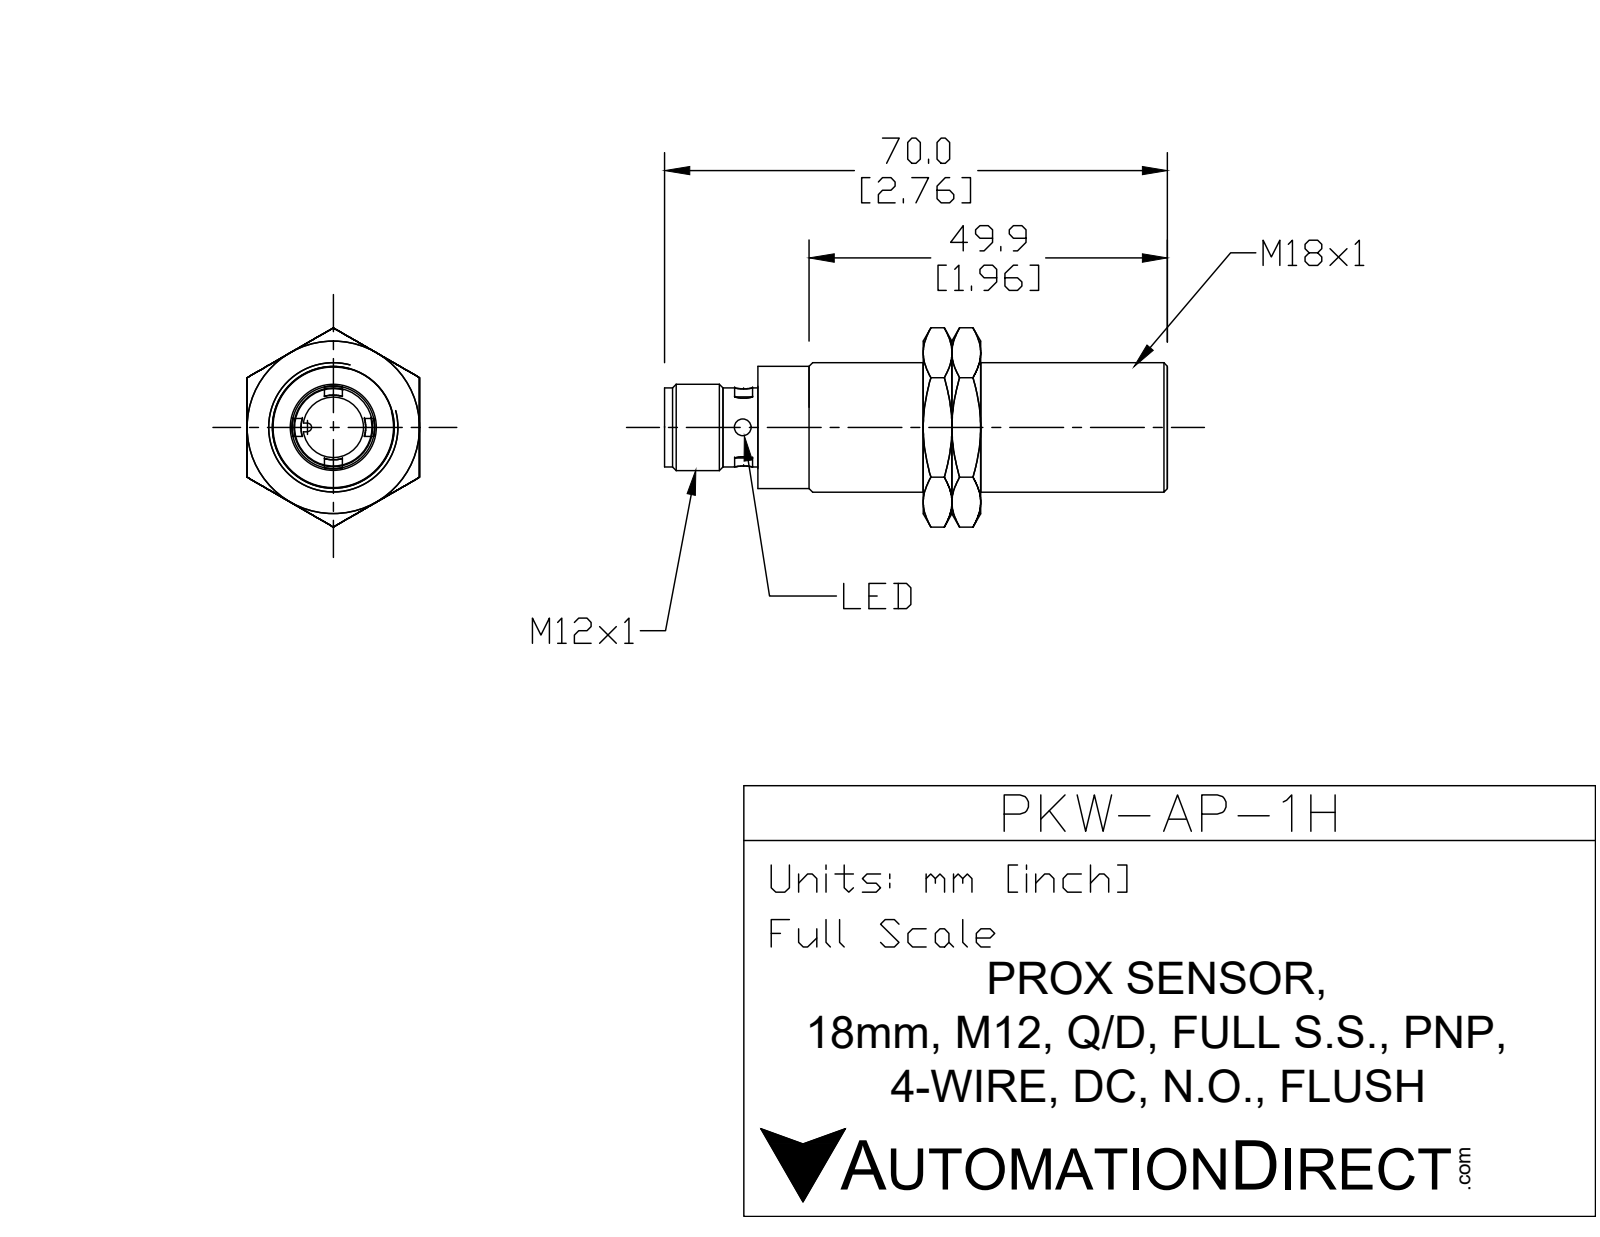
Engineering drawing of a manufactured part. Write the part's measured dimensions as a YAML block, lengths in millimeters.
part_name: "PKW-AP-1H"
step_written_by: "SolidWorks 2017 (AUTOMOTIVE_DESIGN)"
units: millimeters
bodies: {solids: 3, faces: 91, planar: 22, cylindrical: 29, other: 40}
overall_size: [70, 27.7, 24]
volume: 17290
surface_area: 6471
round_holes:
  - {diameter: 2.5, count: 2}
  - {diameter: 8.4, count: 1}
  - {diameter: 16.9, count: 1}
round_bosses_or_shafts:
  - {diameter: 18, count: 1}
  - {diameter: 17, count: 1}
  - {diameter: 12, count: 1}
  - {diameter: 11.5, count: 1}
  - {diameter: 11, count: 1}
partial_cylinders:
  - {radius: 0.6, count: 1}
  - {radius: 4.5, count: 1}
face_to_face_distances: [4, 24, 30, 26, 8, 34, 23, 27, 31, 57]
